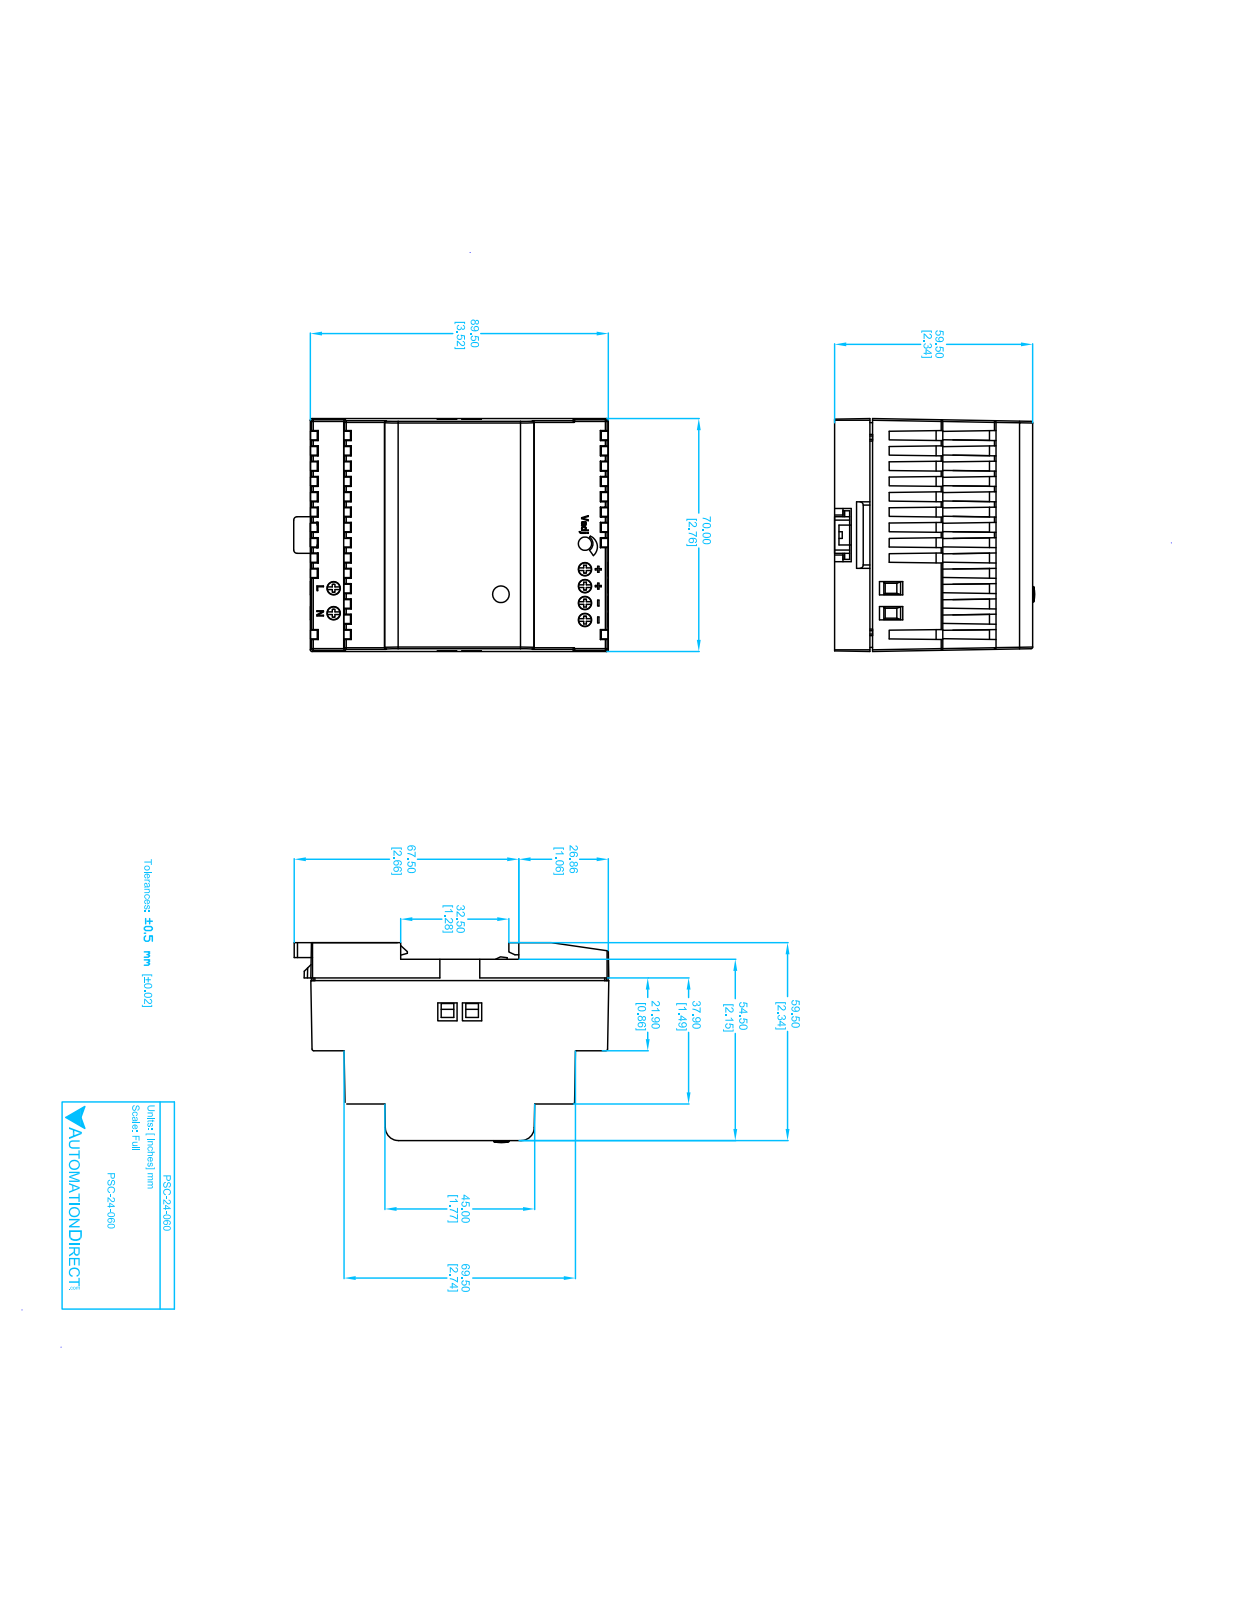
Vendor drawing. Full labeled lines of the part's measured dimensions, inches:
Part name (STEP PRODUCT): PSC-24-060
STEP written by: SolidWorks 2011 (CONFIG_CONTROL_DESIGN)
Units: inches
Bodies: 1 solid, 709 faces (578 planar, 95 cylindrical, 36 other)
Overall size (bounding box): 3.719 × 2.759 × 2.372
Volume: 17.07 in³ · Surface area: 62.88 in²
Round holes (diameter × count): ⌀0.16 ×7
Round bosses / shafts (diameter × count): ⌀0.2 ×1
Partial cylindrical surfaces — rounded edges, fillets, slot ends (radius × count): R0.02 ×26, R0.04 ×2, R0.16 ×2
Main face-to-face distances: 0.19, 0.595, 2.341, 2.151, 0.177, 0.419, 1.9, 1.71, 0.441, 2.759
Hole centre spacings: 0.2, 0.4, 0.25, 0.3, 0.45, 0.6, 0.65, 0.85
